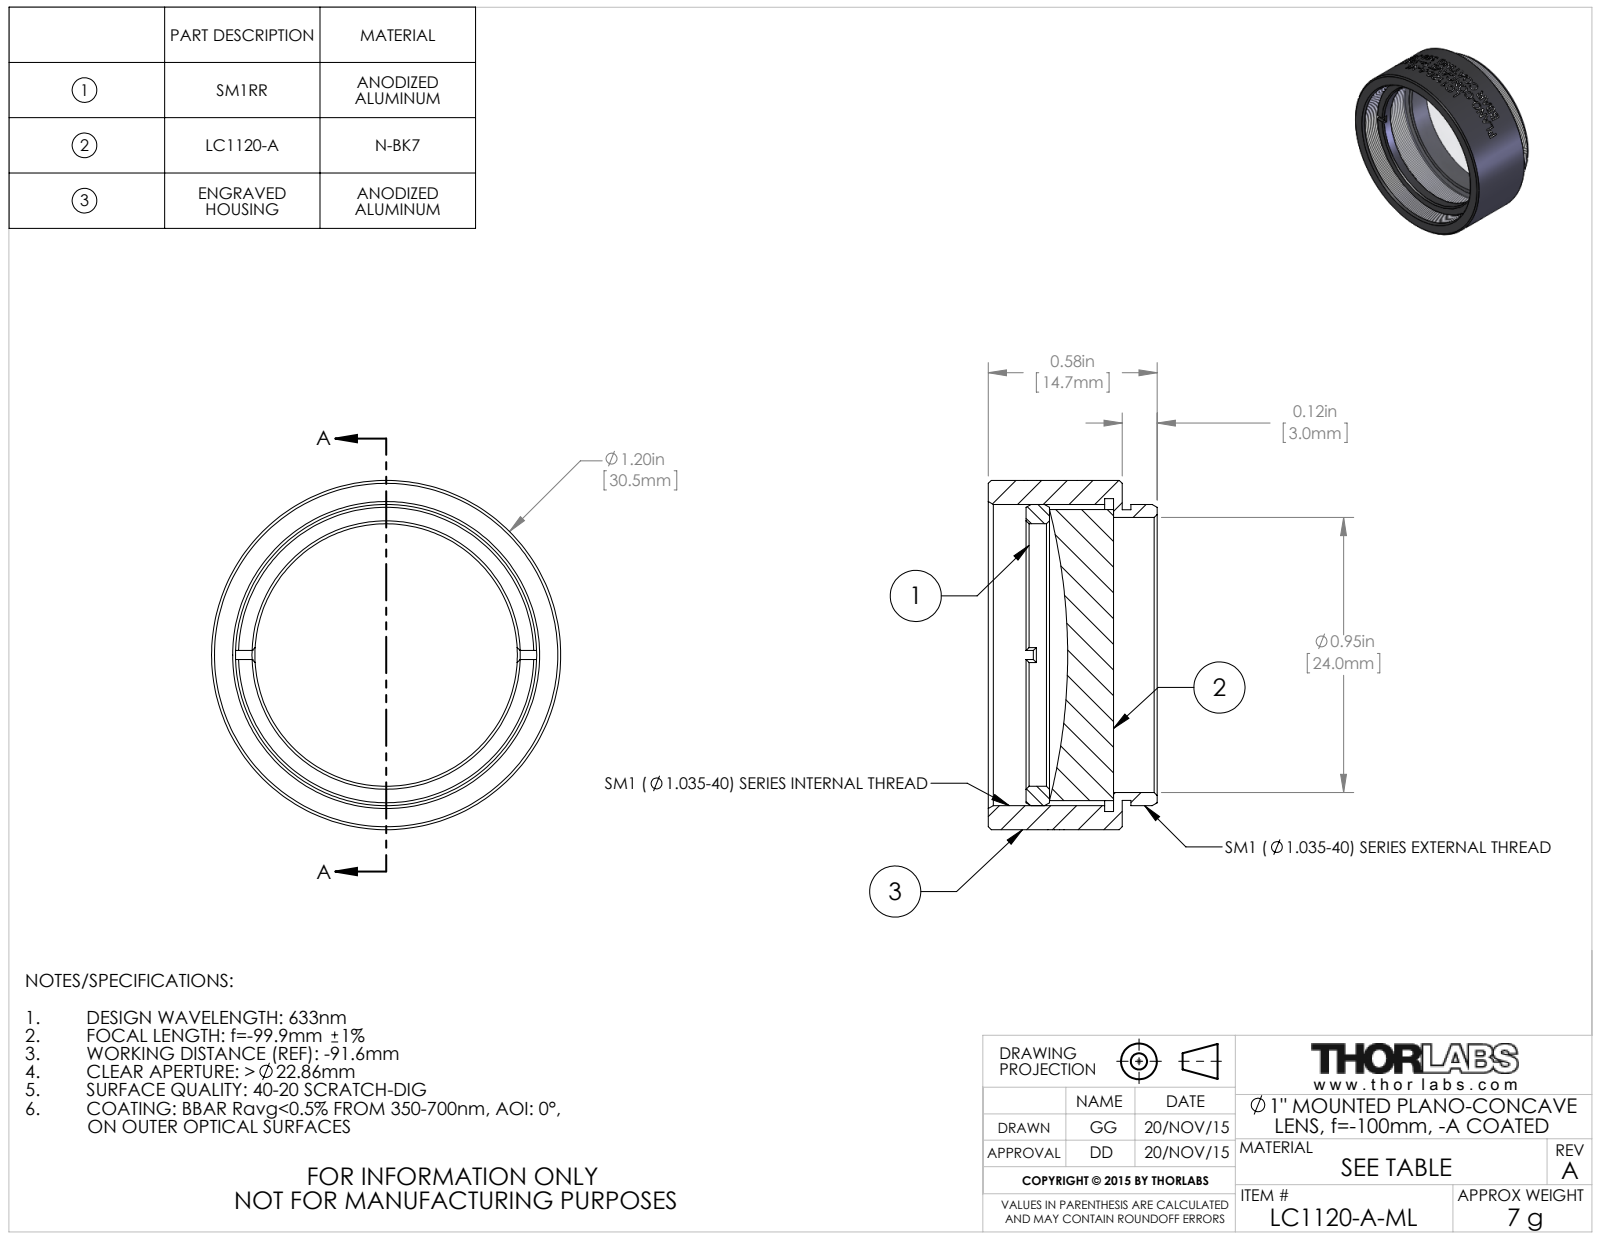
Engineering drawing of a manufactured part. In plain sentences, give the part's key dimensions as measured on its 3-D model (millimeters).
The part is named "TTN045313-E0W". Its 3-D file was written by "SolidWorks 2014 (CONFIG_CONTROL_DESIGN)". It is 3 solids with 152 faces: 20 planar, 108 cylindrical and 24 other. Overall it measures 30.5 by 30.5 by 14.7 millimeters. Its volume is 5 130 cubic millimeters and its surface area 5 196 square millimeters. Round holes: 1 of diameter 22.9, 1 of diameter 24, 1 of diameter 27.3. Round bosses or shafts: 1 of diameter 30.5, 1 of diameter 26.3, 1 of diameter 25.4, 1 of diameter 25.4. The main face-to-face distances are 0.8, 11.7, 10.9, 6.4, 5.6, 5.3, 8.4, 7.6, 2, 3.3.
